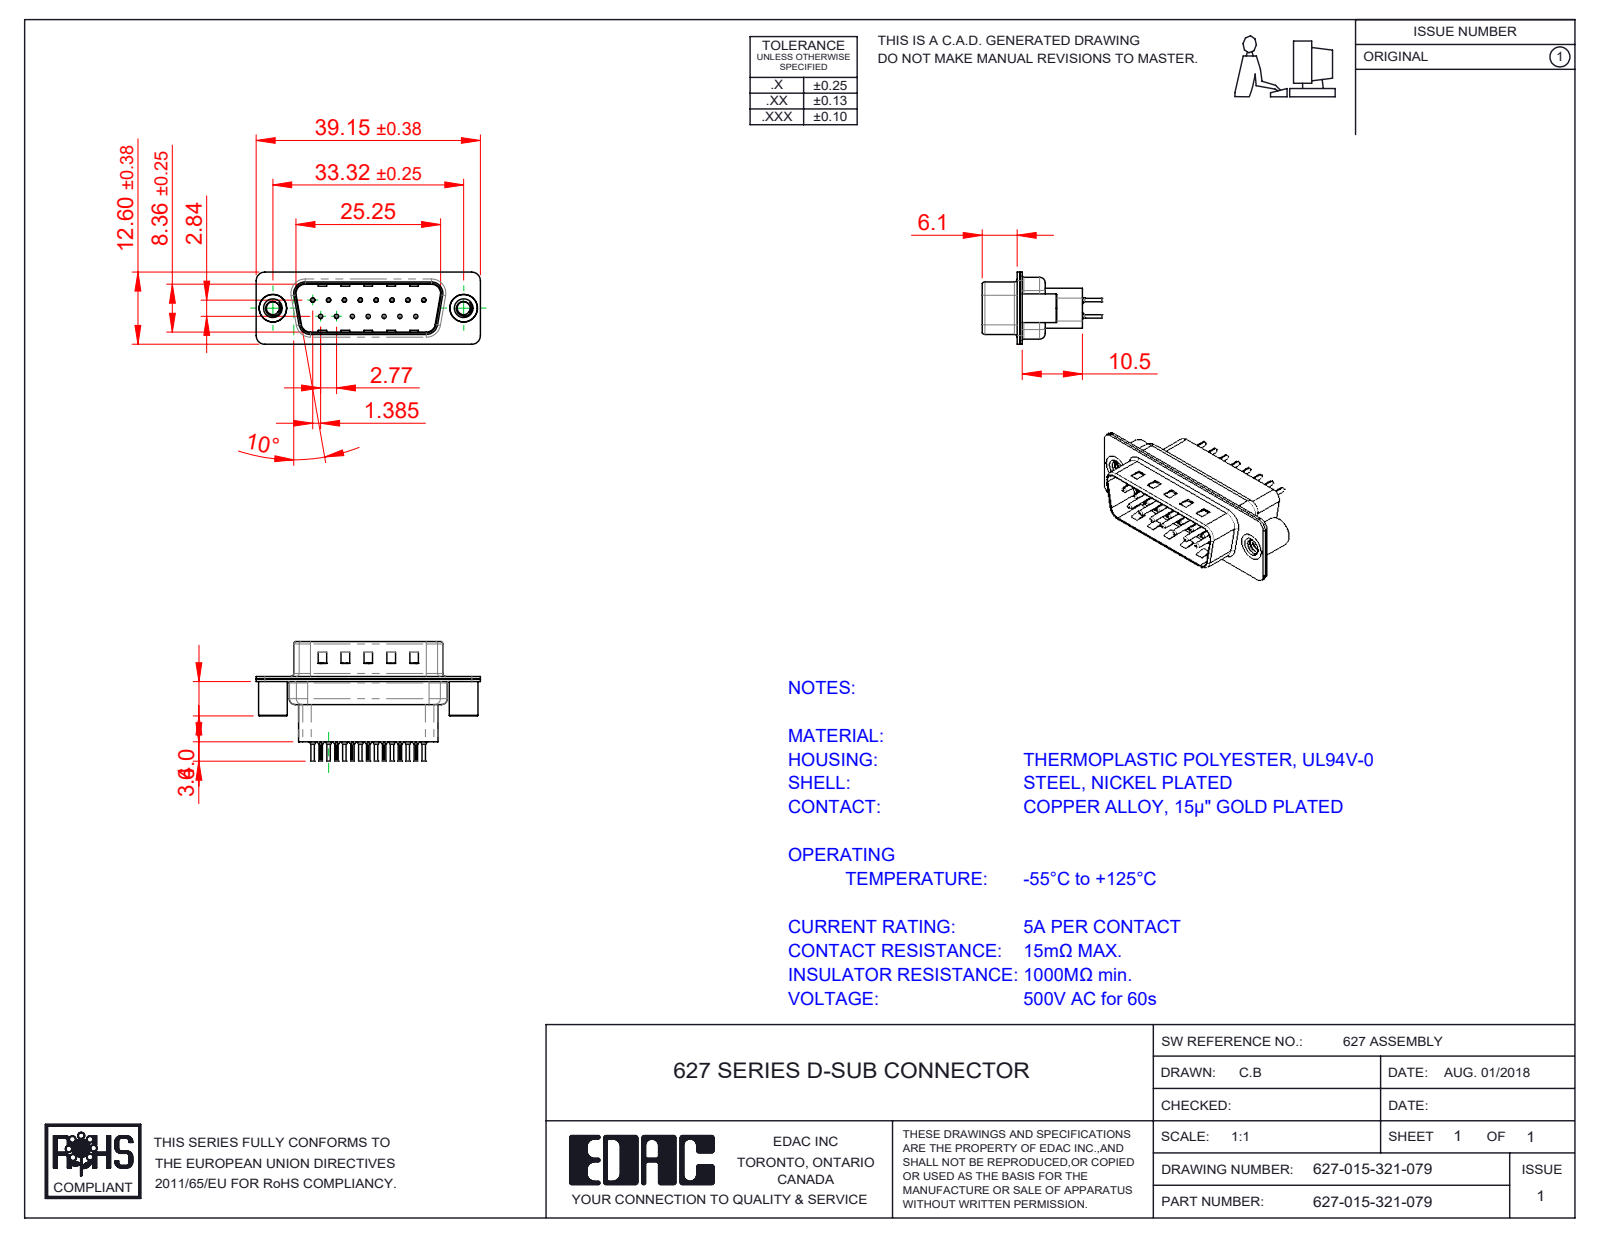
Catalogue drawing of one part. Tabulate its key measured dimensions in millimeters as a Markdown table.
| quantity | value |
| --- | --- |
| part name | 627 Contact Row 2_21H; 627-015-321-079; 627 Shell Rear_15 Contacts; 627 Contact Row 1_21H (+3 more) |
| STEP written by | SolidWorks 2020 (CONFIG_CONTROL_DESIGN) |
| units | millimeters |
| bodies | 20 solids, 1832 faces (499 planar, 708 cylindrical, 625 other) |
| overall size | 39.15 × 20.8 × 12.6 |
| volume | 2 635 mm³ |
| surface area | 6 801 mm² |
| round holes (diameter × count) | 0.2 × 15, 0.35 × 15, 1.1 × 15, 1.6 × 15, 2.26 × 2, 4 × 2, 4.8 × 2 |
| round bosses / shafts (diameter × count) | 2 × 15, 1.5 × 15, 0.75 × 15, 0.6 × 15, 5 × 2, 4.9 × 2 |
| partial cylindrical surfaces (radius × count) | 0.1 × 30, 1.5 × 16, 2 × 12, 0.5 × 8, 1.6 × 8, 0.25 × 4, 0.6 × 4, 0.65 × 4 |
| main face-to-face distances | 0.4, 0.45, 0.9, 0.82, 9.58, 1.5, 0.68, 7.68, 1.4, 1.08 |
| hole center spacings | 3.16, 2.77, 5.54, 8.31, 11.08, 5.03, 5.04, 7.48 |
